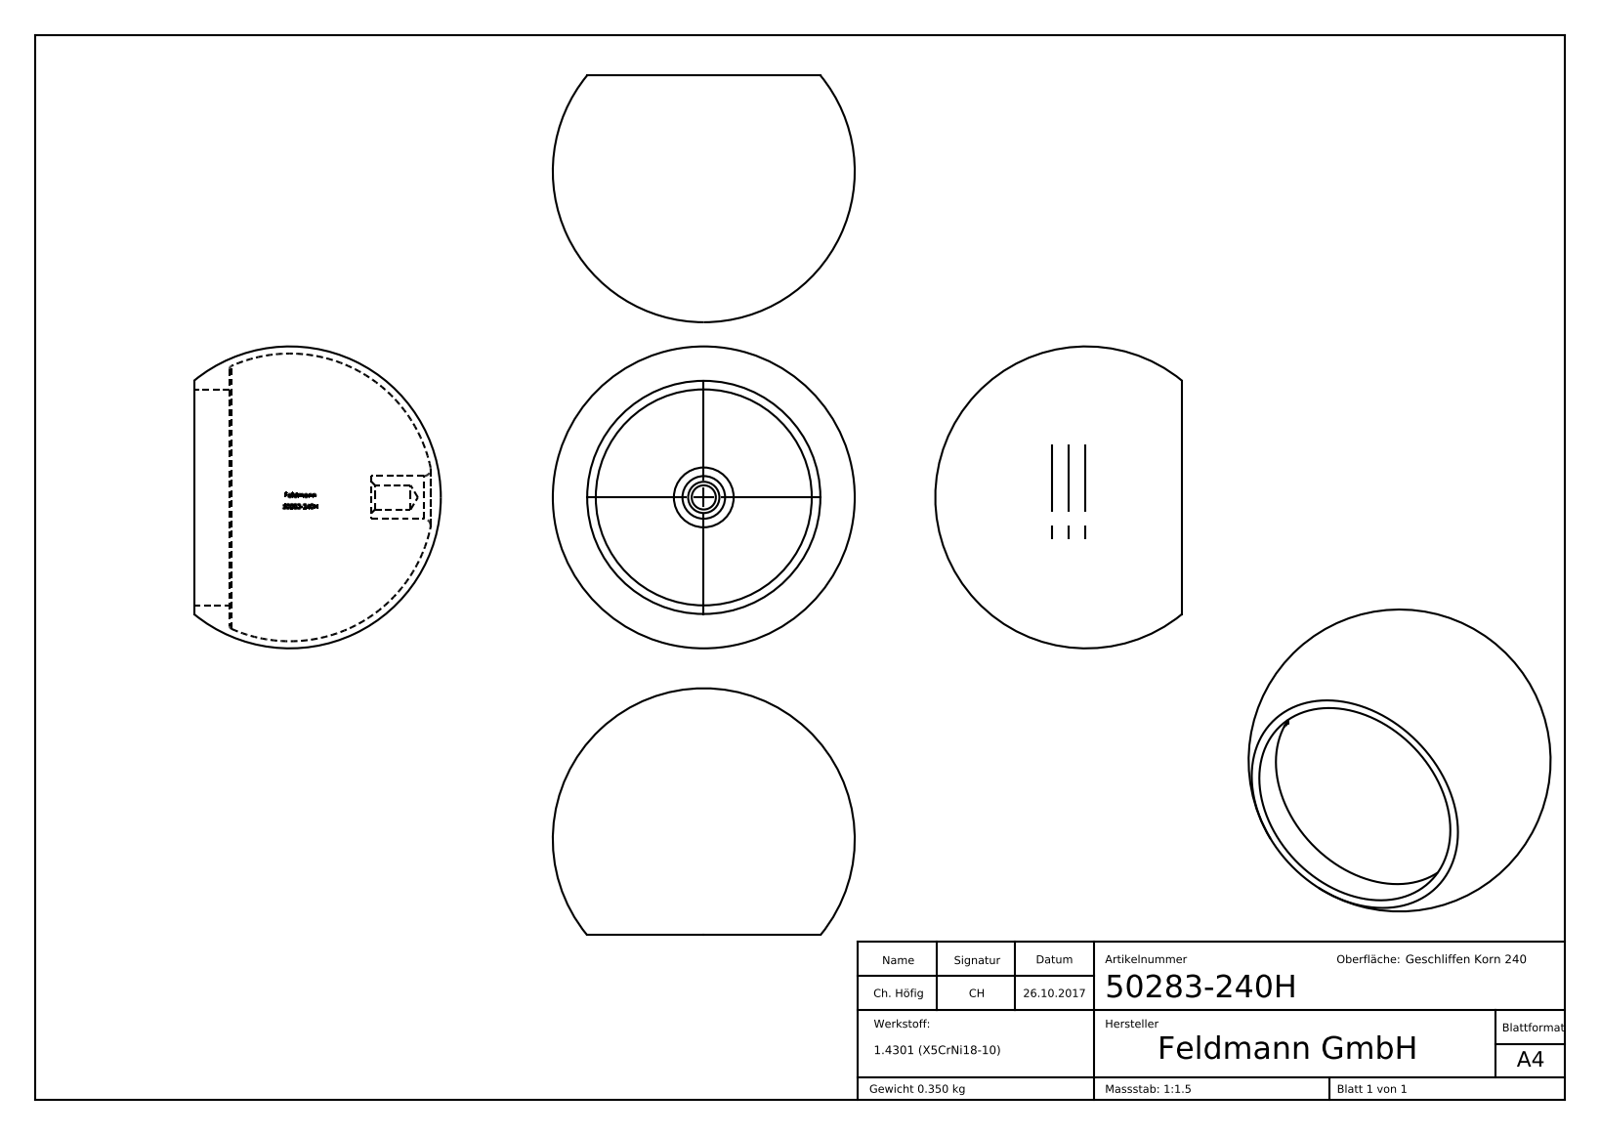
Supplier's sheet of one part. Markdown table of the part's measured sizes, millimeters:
| quantity | value |
| --- | --- |
| part name | 50283-240H |
| STEP written by | SolidWorks 2015 (CONFIG_CONTROL_DESIGN) |
| units | millimeters |
| bodies | 1 solid, 270 faces (107 planar, 6 cylindrical, 157 other) |
| overall size | 85 × 85 × 69.5 |
| volume | 44 344 mm³ |
| surface area | 37 726 mm² |
| round holes (diameter × count) | 6.8 × 1, 60.8 × 1 |
| round bosses / shafts (diameter × count) | 12 × 1 |
| main face-to-face distances | 10, 40, 50, 3.2, 6.98, 3.4, 0.68, 8.2, 2.32, 4.66 |
